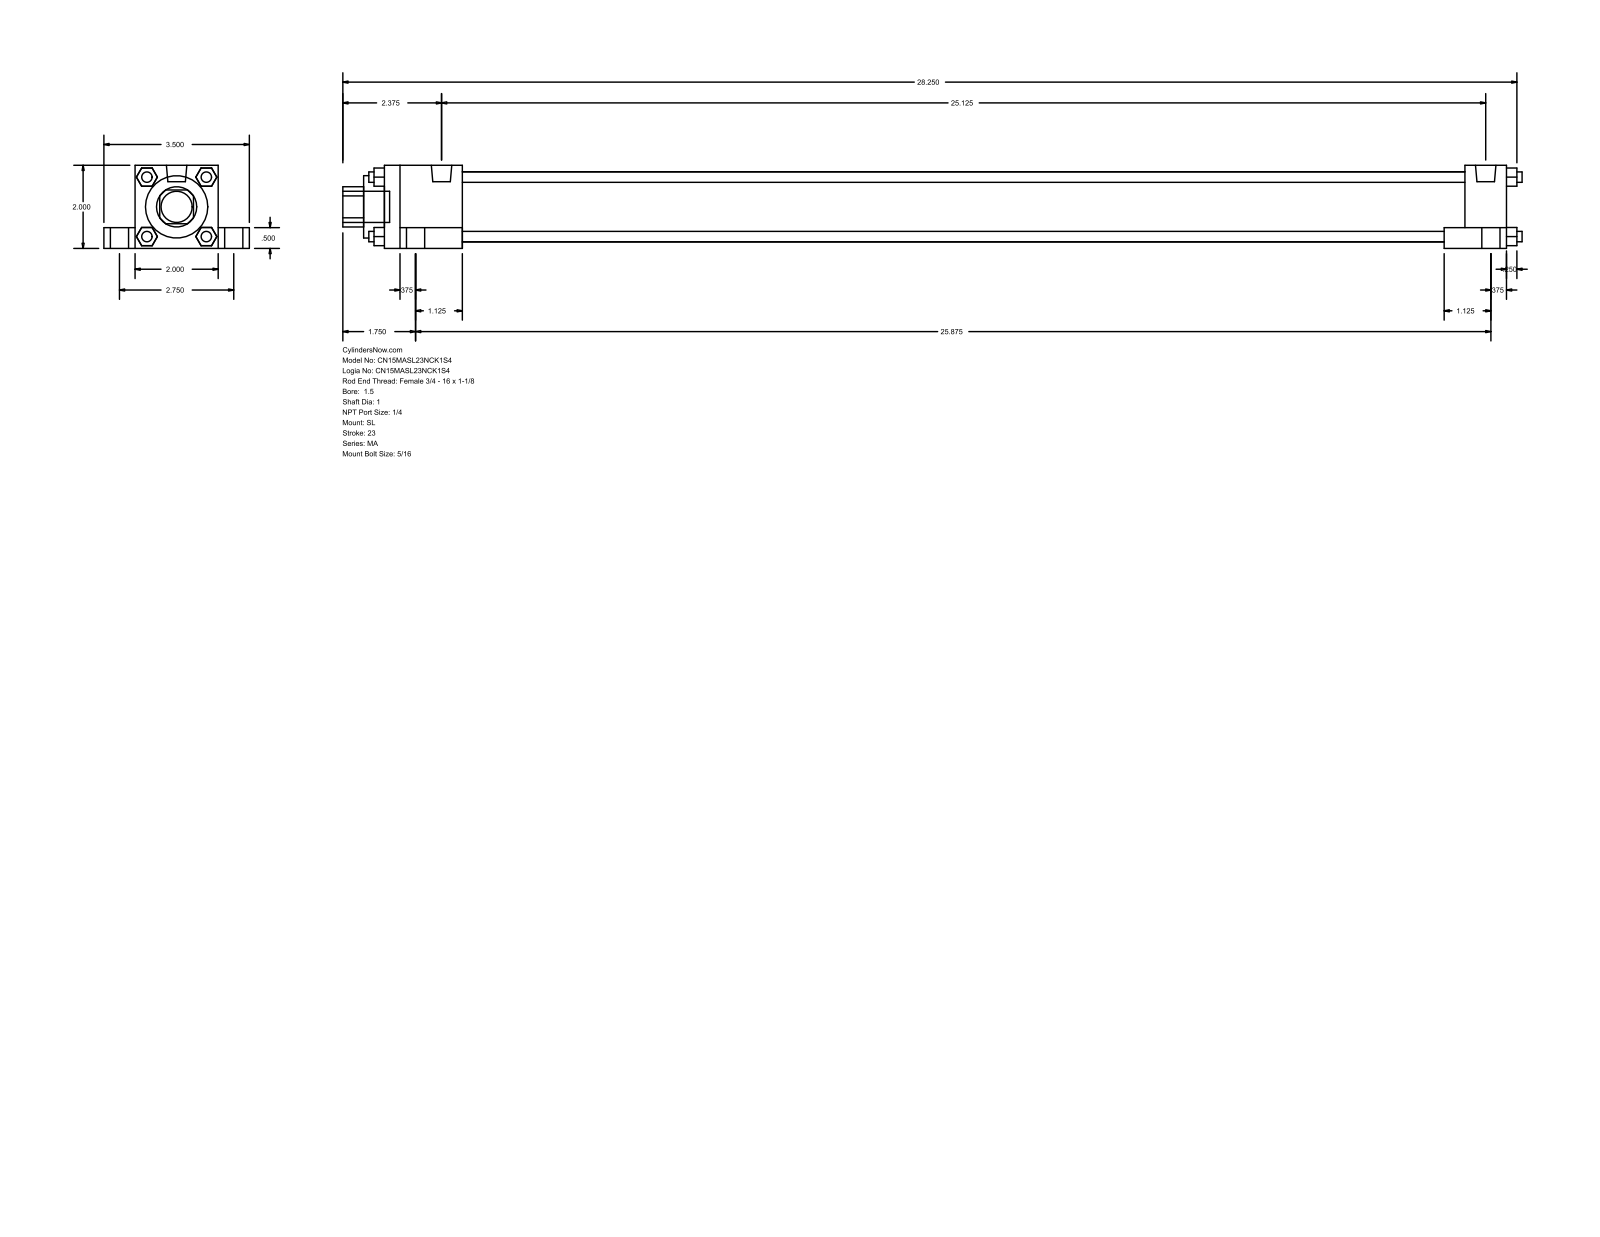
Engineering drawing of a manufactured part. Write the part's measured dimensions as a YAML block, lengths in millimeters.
part_name: "MA_SL__0150_1"
step_written_by: "GSSL Pune (CONFIG_CONTROL_DESIGN)"
units: millimeters
bodies: {solids: 0, faces: 148, planar: 112, cylindrical: 36, other: 0}
overall_size: [720.73, 88.9, 50.8]
round_holes:
  - {diameter: 25.4, count: 1}
  - {diameter: 38.1, count: 1}
  - {diameter: 42.93, count: 1}
round_bosses_or_shafts:
  - {diameter: 17.46, count: 4}
  - {diameter: 11.11, count: 4}
  - {diameter: 7.94, count: 4}
  - {diameter: 6.35, count: 4}
  - {diameter: 12.49, count: 2}
  - {diameter: 19.05, count: 1}
partial_cylinders:
  - {radius: 12.29, count: 1}
face_to_face_distances: [50.8, 12.7, 19.05, 69.85, 9.52, 38.1, 6.35, 685.8, 25.4, 660.4]
